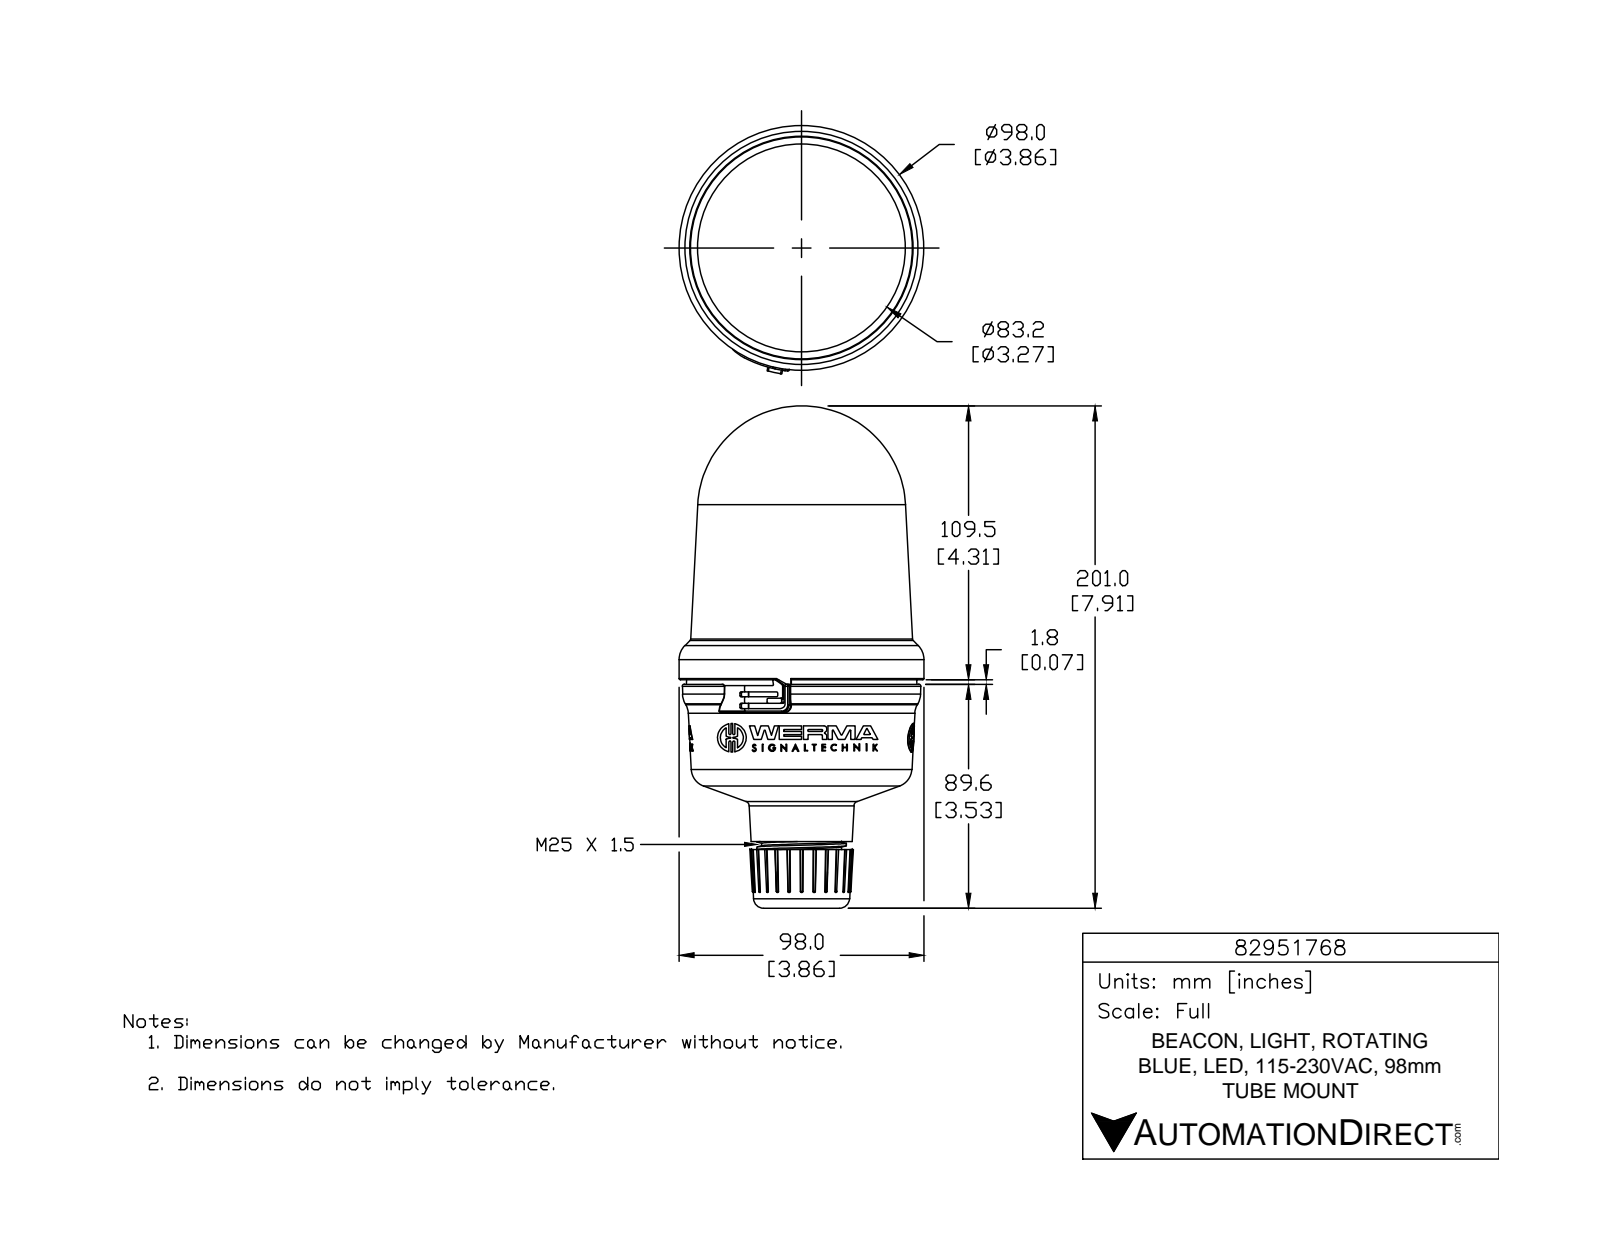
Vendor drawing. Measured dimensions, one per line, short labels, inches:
name: 82951768
written by: SolidWorks 2015 (AUTOMOTIVE_DESIGN)
unit: in
bodies: 1 solid, 1006 faces (554 planar, 189 cylindrical, 263 other)
size: 7.914 × 3.912 × 3.858
volume: 54.7 in³; area: 91.39 in²
holes: 3× ⌀0.078, 1× ⌀1.013, 1× ⌀1.024
bosses: 3× ⌀0.452, 3× ⌀0.113, 1× ⌀3.858, 1× ⌀1.409, 1× ⌀1.261
rounds: 12× R0.02, 9× R0.007, 6× R0.007, 6× R0.016, 6× R0.016, 6× R0.016, 6× R0.262, 3× R0.006
face distances: 2.214, 0.462, 2.676, 0.335, 0.127, 2.548, 2.603, 2.476, 2.141, 0.073
